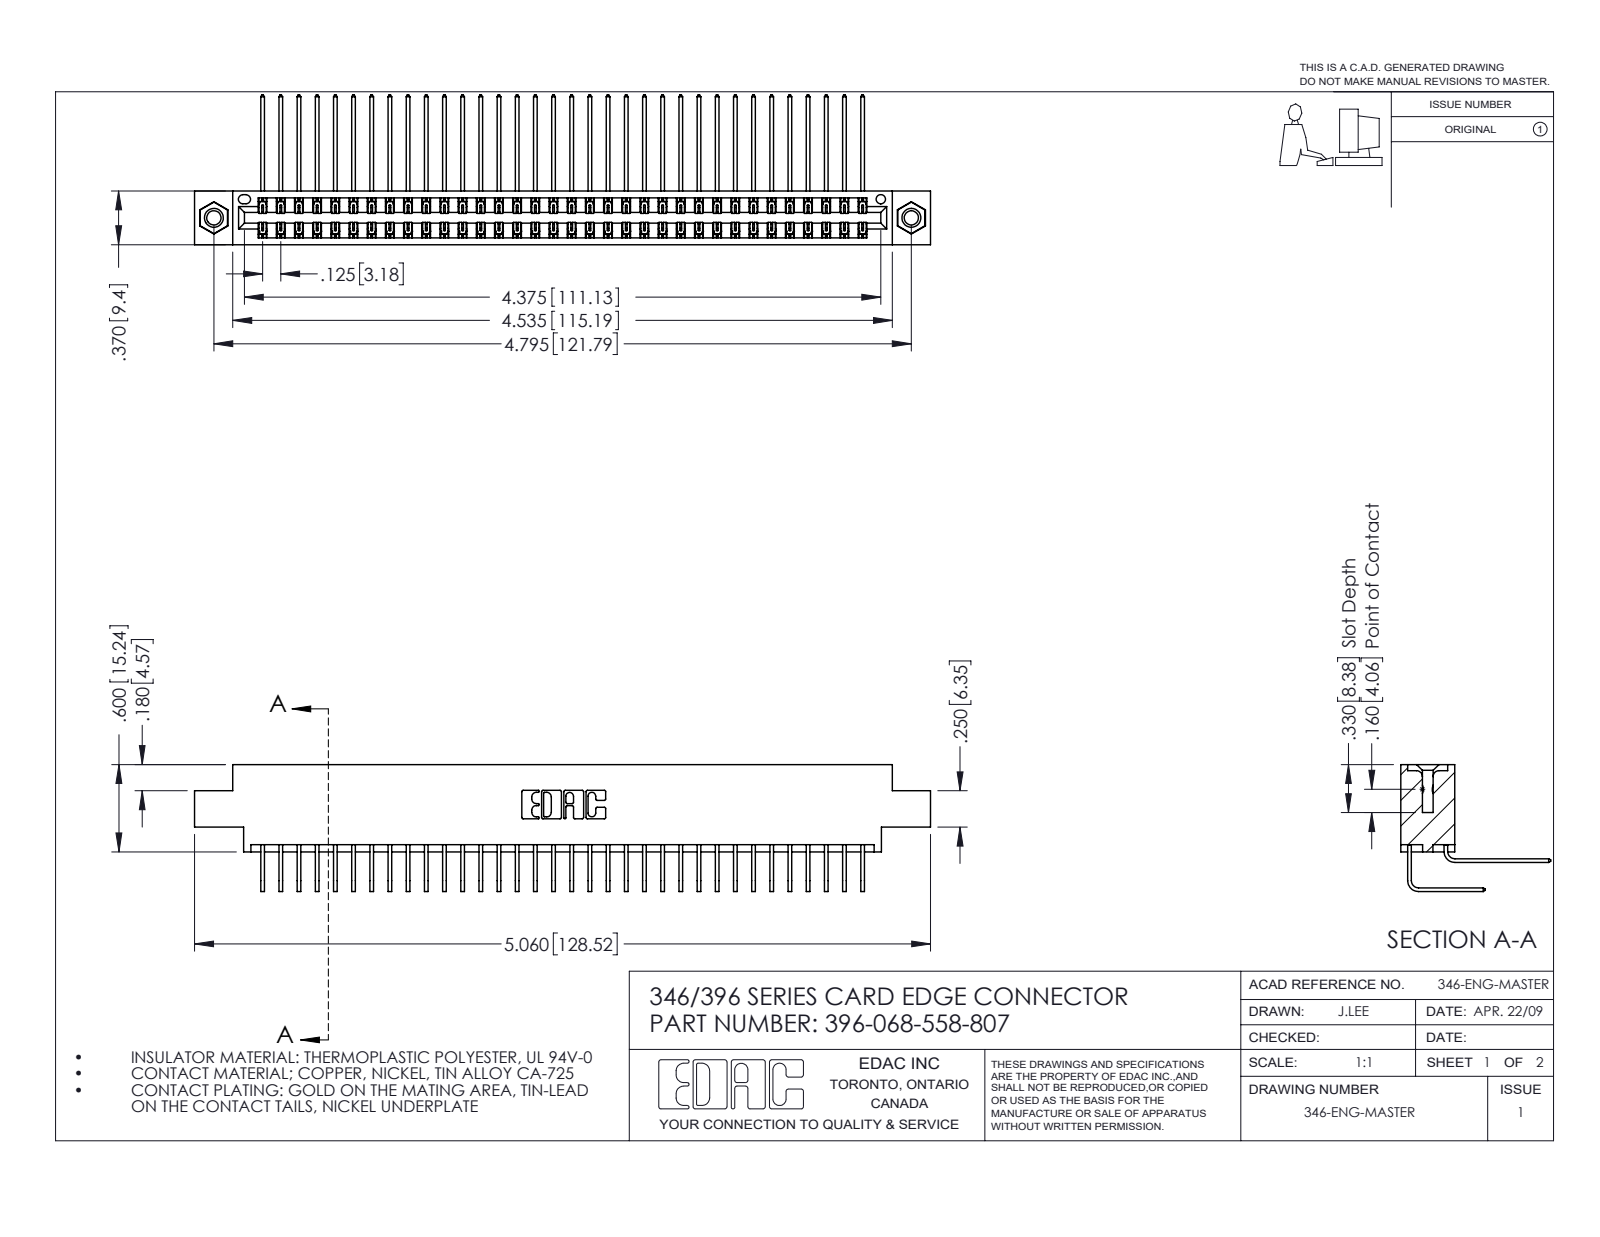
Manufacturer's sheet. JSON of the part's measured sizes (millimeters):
{"part_name": "345-250-001_345-250-005-103; 346 Part_0.170 Offset - 0.156 Dia-TI; 345-292-001_558 Tail - 2; 345-292-001_558 559 Tail - 1 (+1 more)", "step_written_by": "SolidWorks 2016 (CONFIG_CONTROL_DESIGN)", "units": "millimeters", "bodies": {"solids": 71, "faces": 3858, "planar": 2628, "cylindrical": 1214, "other": 16}, "overall_size": [128.5, 26.2, 22.2], "volume_mm3": 12700, "surface_area_mm2": 19420, "round_holes": [[2.5, 2], [3.2, 2], [4, 2], [1.6, 1]], "round_bosses_or_shafts": [[3.9, 2]], "partial_cylinders_radius": [[0.2, 102], [0.3, 22], [0.2, 6], [0.8, 6], [0.7, 3], [0.4, 2], [0.6, 2], [0.6, 2]], "face_to_face_distances": [8.2, 1.2, 0.6, 9.4, 6.4, 7.6, 1.8, 7, 5.6, 3.8], "hole_center_spacings": [6.2, 116.5, 121.8]}
